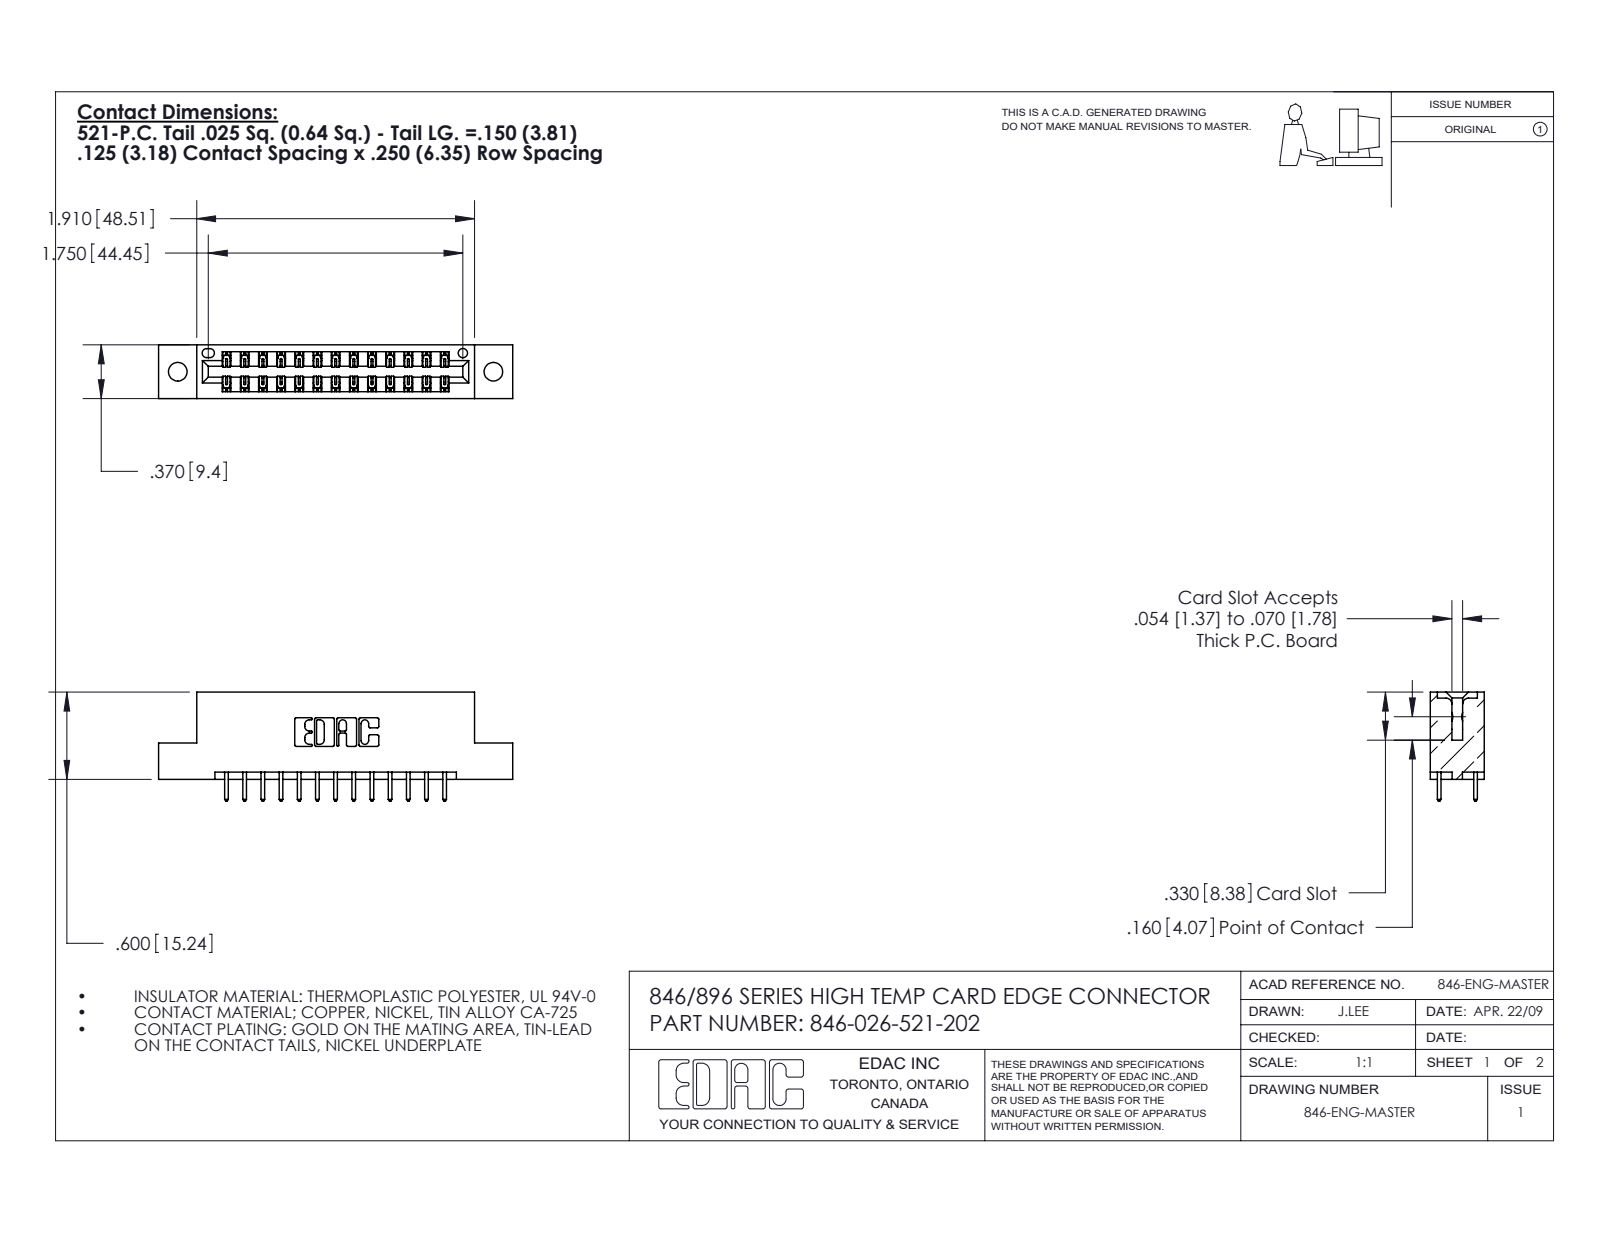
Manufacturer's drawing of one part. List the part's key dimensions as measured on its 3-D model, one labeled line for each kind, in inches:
Part name (STEP PRODUCT): 345-292-001_345-293-121; 346-026-521-202; 346 Part_Flush Mounting Lugs - 0.128 Dia
STEP written by: SolidWorks 2016 (CONFIG_CONTROL_DESIGN)
Units: inches
Bodies: 27 solids, 1474 faces (986 planar, 488 cylindrical, 0 other)
Overall size (bounding box): 2.435 × 0.75 × 0.37
Volume: 0.351 in³ · Surface area: 11.03 in²
Round holes (diameter × count): ⌀0.128 ×2, ⌀0.064 ×1
Partial cylindrical surfaces — rounded edges, fillets, slot ends (radius × count): R0.006 ×39, R0.01 ×26, R0.01 ×22, R0.007 ×6, R0.031 ×6, R0.026 ×3, R0.014 ×2, R0.022 ×2
Main face-to-face distances: 0.25, 0.048, 0.322, 0.37, 0.072, 0.298, 0.025, 0.275, 0.148, 0.222
Hole centre spacings: 0.246, 1.964, 2.17
